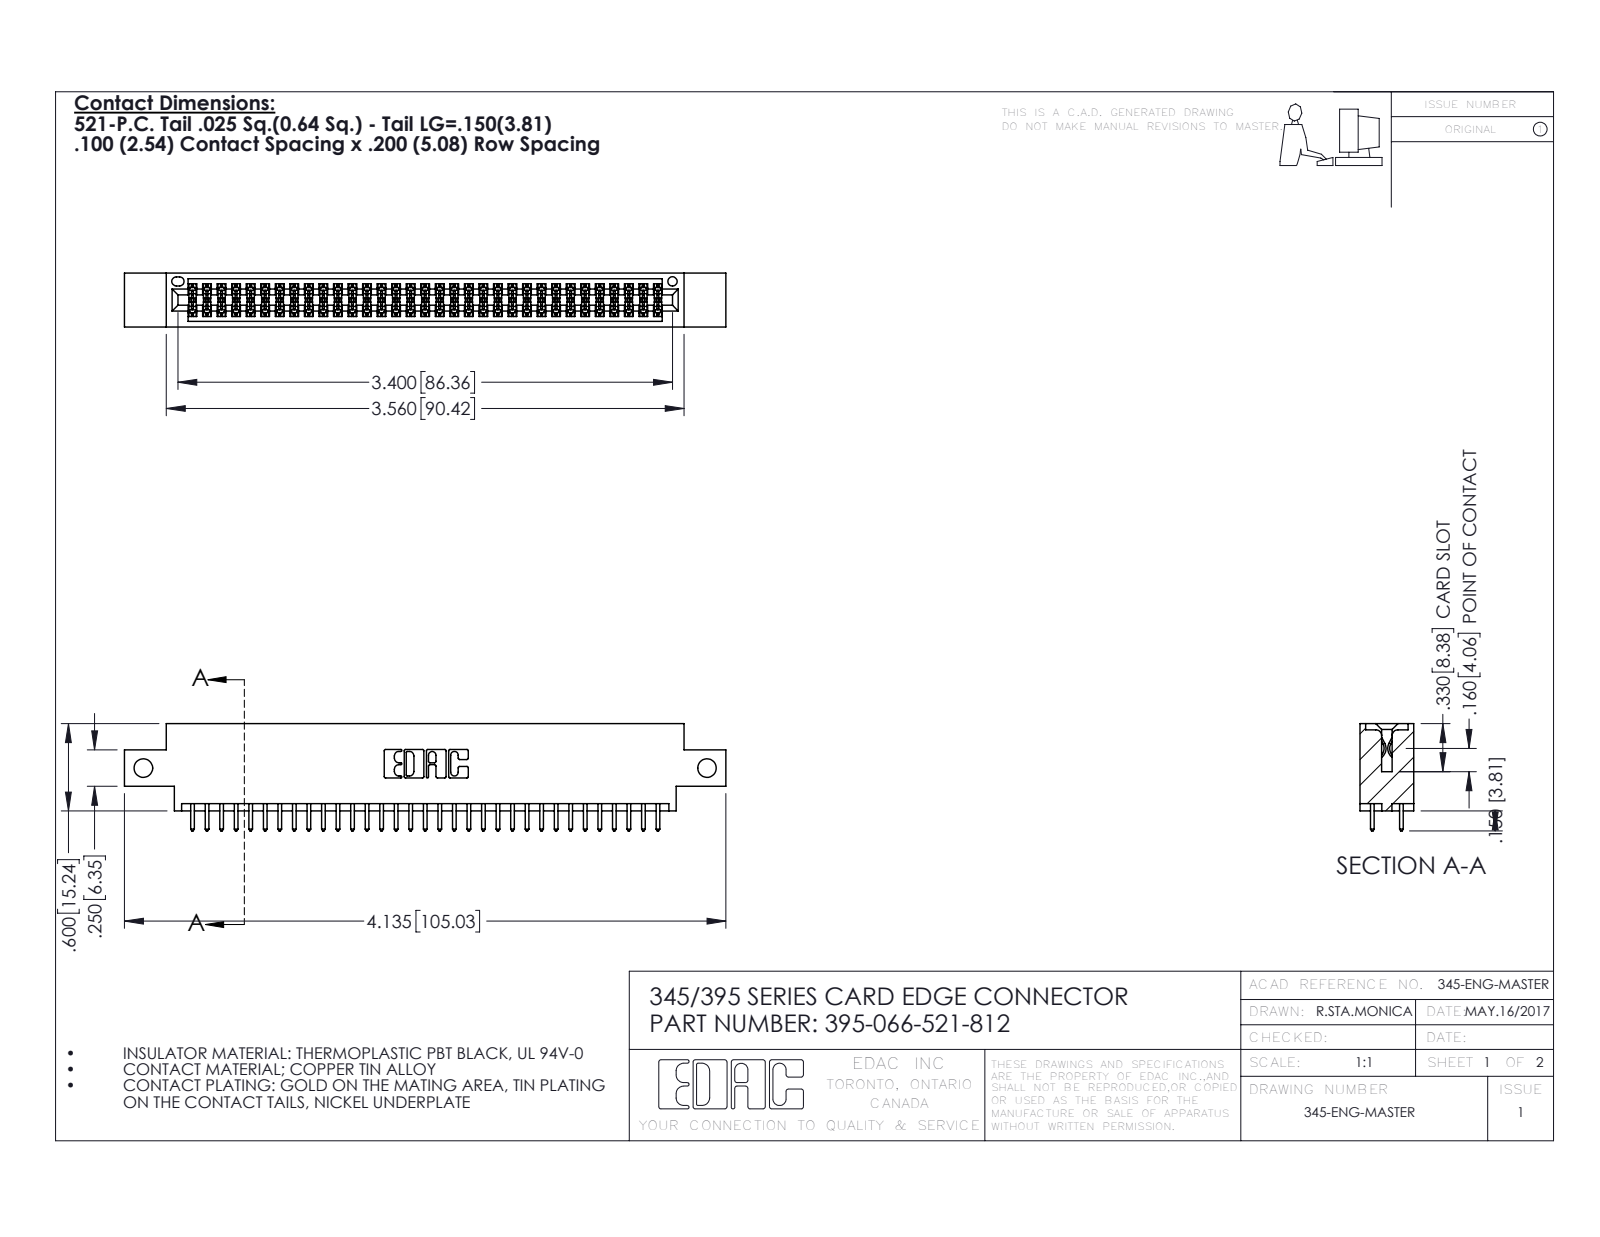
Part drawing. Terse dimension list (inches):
name: 345-292-001_345-293-121; 345 Part_0.170 Offset - Side Mount; 395-066-521-812
written by: SolidWorks 2016 (CONFIG_CONTROL_DESIGN)
unit: in
bodies: 67 solids, 3430 faces (2262 planar, 1168 cylindrical, 0 other)
size: 4.135 × 0.737 × 0.37
volume: 0.604 in³; area: 22.13 in²
holes: 2× ⌀0.128, 1× ⌀0.064
rounds: 99× R0.006, 66× R0.01, 22× R0.01, 6× R0.007, 6× R0.031, 3× R0.026, 2× R0.014, 2× R0.019
face distances: 0.298, 0.072, 0.37, 0.2, 0.098, 0.272, 0.025, 0.225, 0.175, 0.149
hole spacings: 3.875
